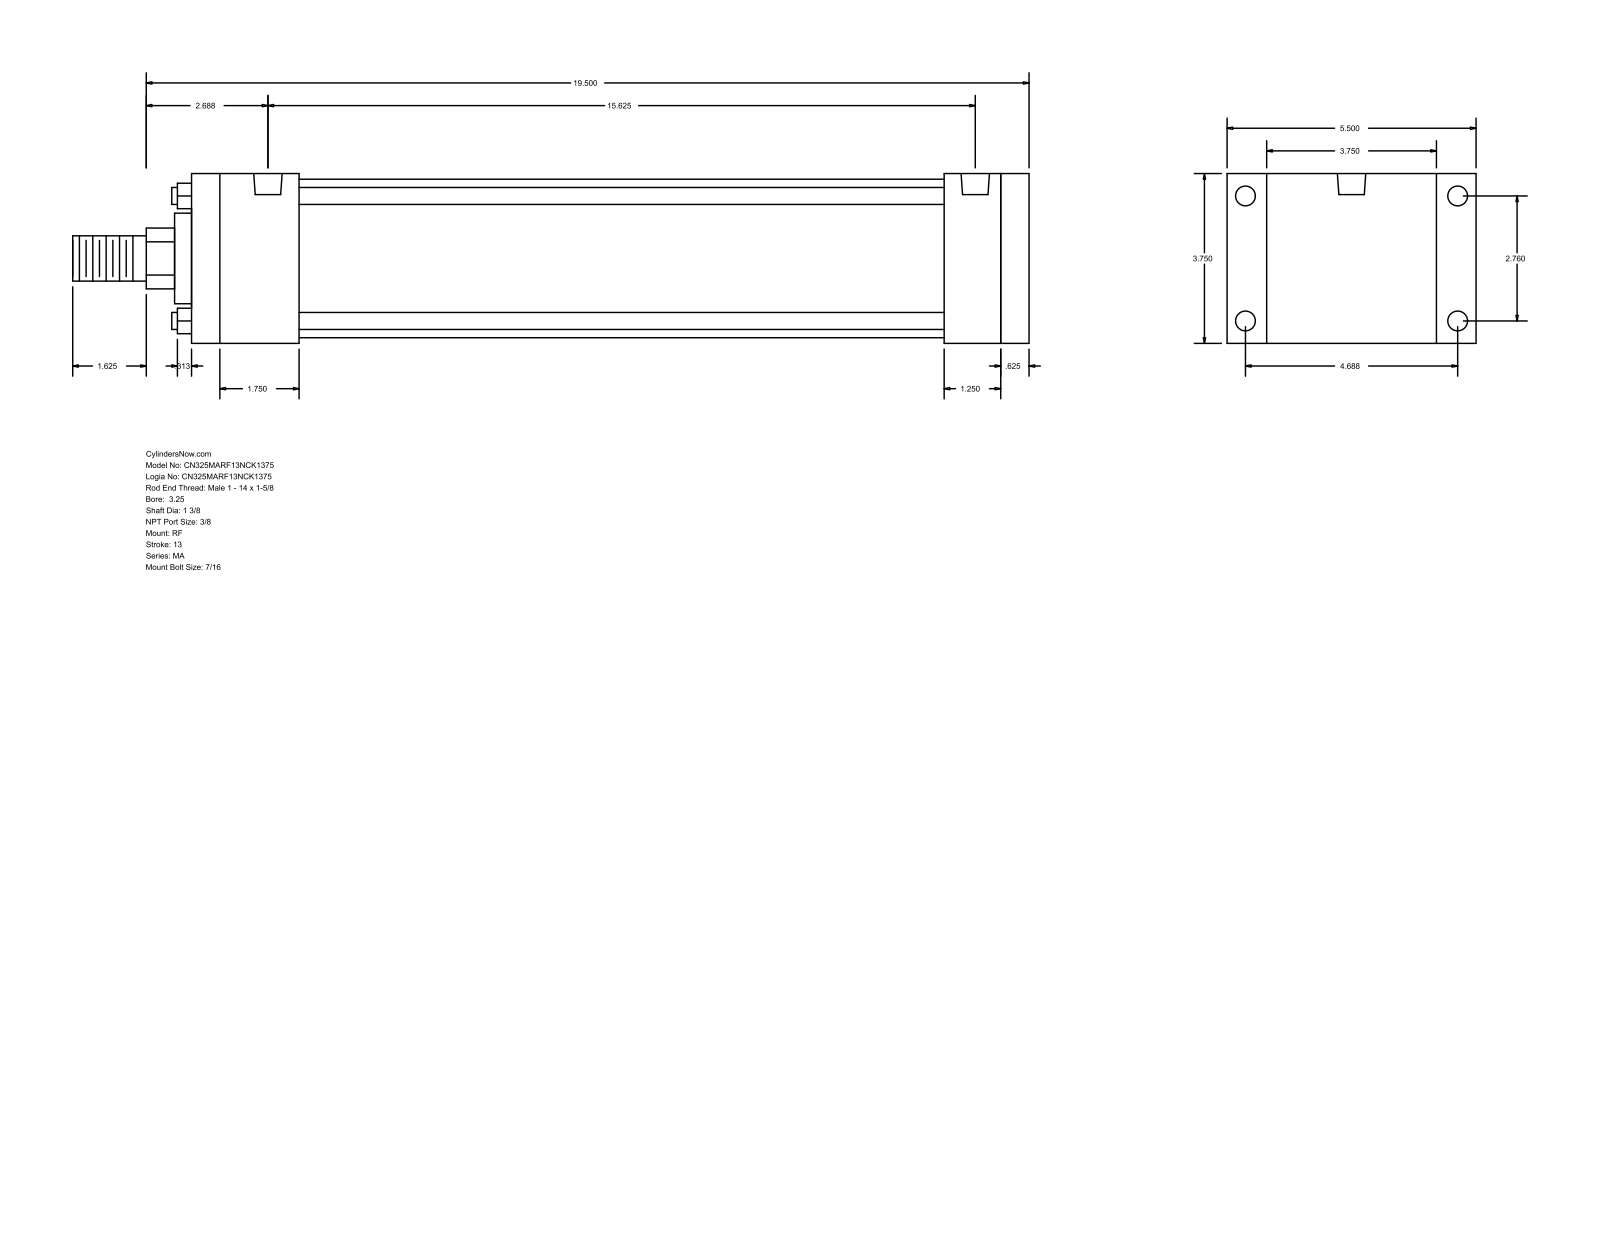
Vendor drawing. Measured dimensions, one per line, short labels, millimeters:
name: MA_RF__0325_1.375
written by: GSSL Pune (CONFIG_CONTROL_DESIGN)
unit: mm
bodies: 0 solids, 92 faces (64 planar, 28 cylindrical, 0 other)
size: 536.58 × 139.7 × 95.25
holes: 8× ⌀11.11, 2× ⌀15.93
bosses: 4× ⌀9.53, 1× ⌀88.9, 1× ⌀50.8, 1× ⌀34.92, 1× ⌀25.4
rounds: 1× R17.06
face distances: 95.24, 469.9, 454.03, 15.87, 22.23, 117.47, 422.28, 31.75, 47.62, 60.32
hole spacings: 70.1, 119.06, 138.16, 387.35, 4.76, 4.77, 392.11, 392.12
